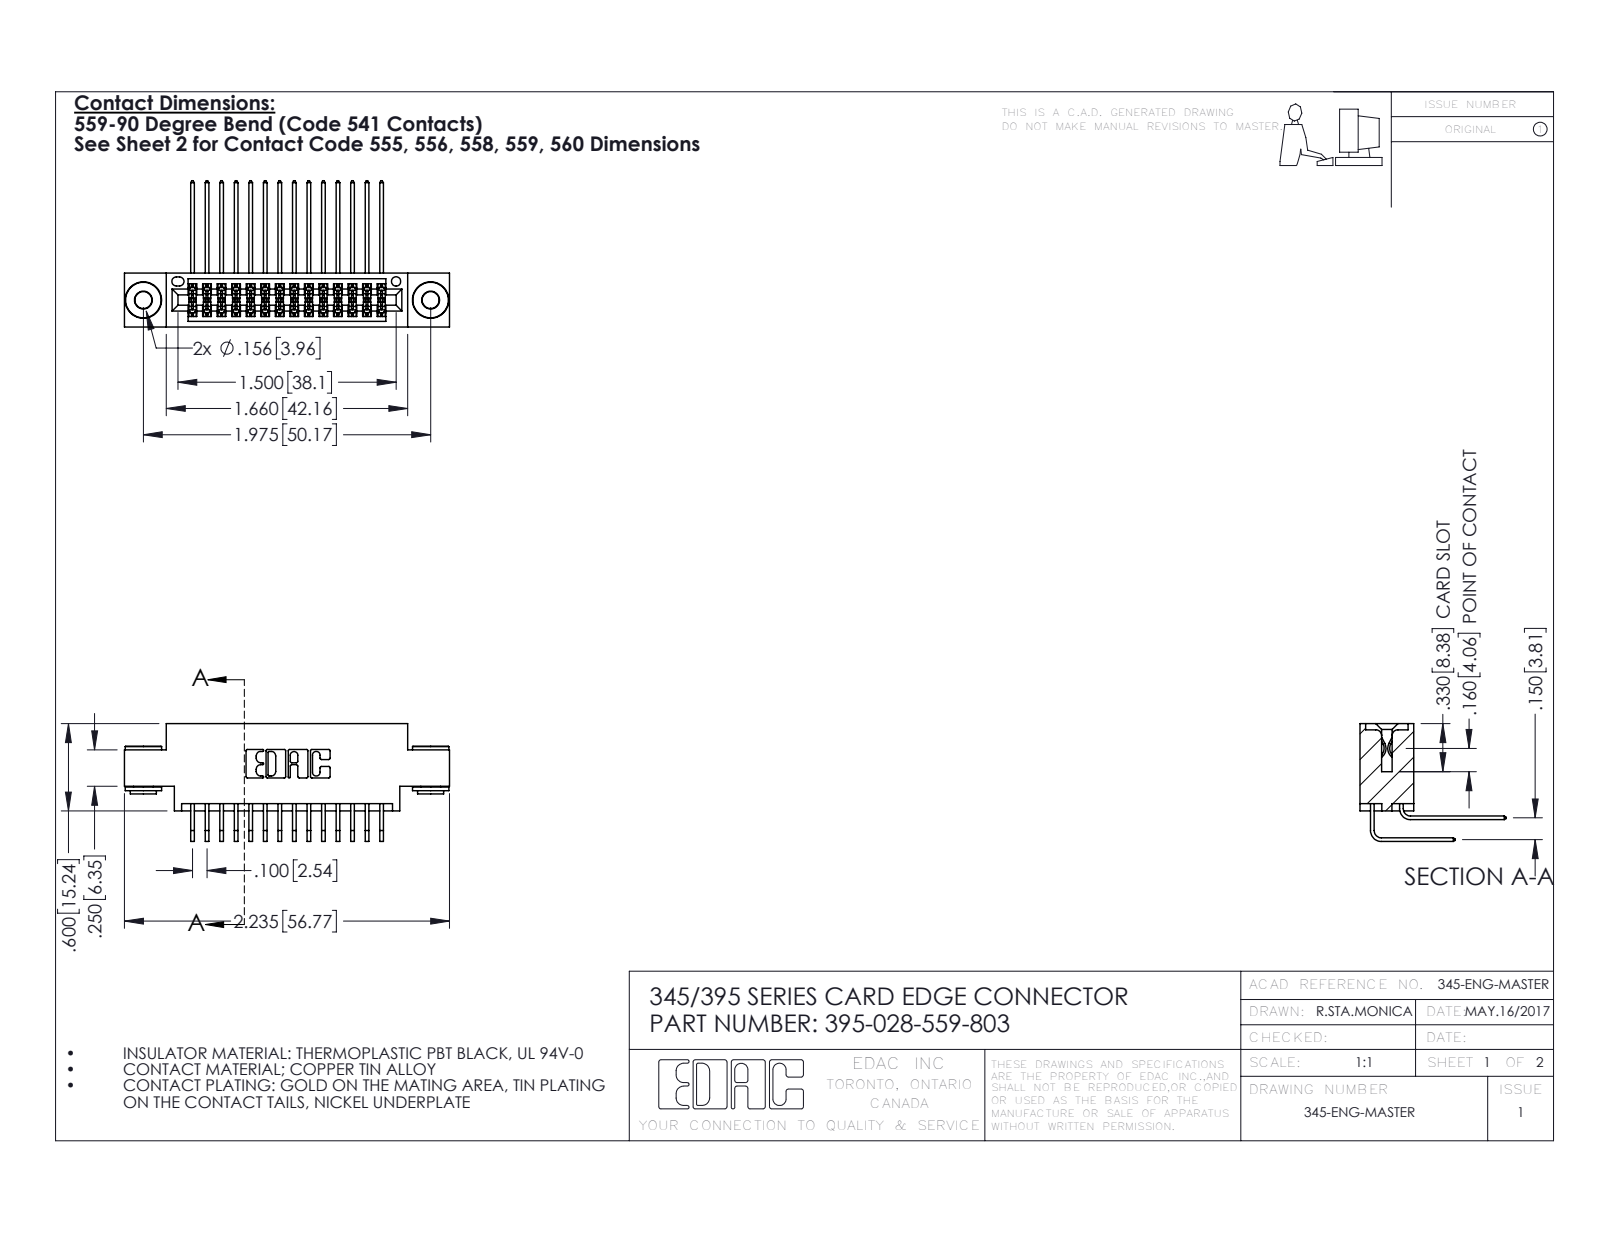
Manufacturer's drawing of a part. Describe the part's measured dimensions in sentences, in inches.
The part is named "345-292-001_558 559 Tail - 1; 345-250-002_345-250-002-102; 395-028-559-803; 345-292-001_559 Tail - 2 (+1 more)". Its 3-D file was written by "SolidWorks 2016 (CONFIG_CONTROL_DESIGN)". It is 31 solids with 1624 faces: 1074 planar, 542 cylindrical and 8 other. Overall it measures 2.235 by 1.005 by 0.809 inches. Its volume is 0.325 cubic inches and its surface area 13.07 square inches. Round holes: 2 of diameter 0.116, 2 of diameter 0.156, 1 of diameter 0.064. Round bosses or shafts: 2 of diameter 0.25, 2 of diameter 0.18, 2 of diameter 0.136. Partial cylindrical surfaces (rounded edges, fillets, slot ends): 42 of radius 0.006, 22 of radius 0.01, 6 of radius 0.007, 6 of radius 0.031, 3 of radius 0.026, 2 of radius 0.014, 2 of radius 0.019, 2 of radius 0.022. The main face-to-face distances are 0.072, 0.298, 0.37, 0.2, 0.098, 0.272, 0.025, 0.175, 0.15, 0.225. The hole center spacings are 0.27, 1.742, 1.975.
